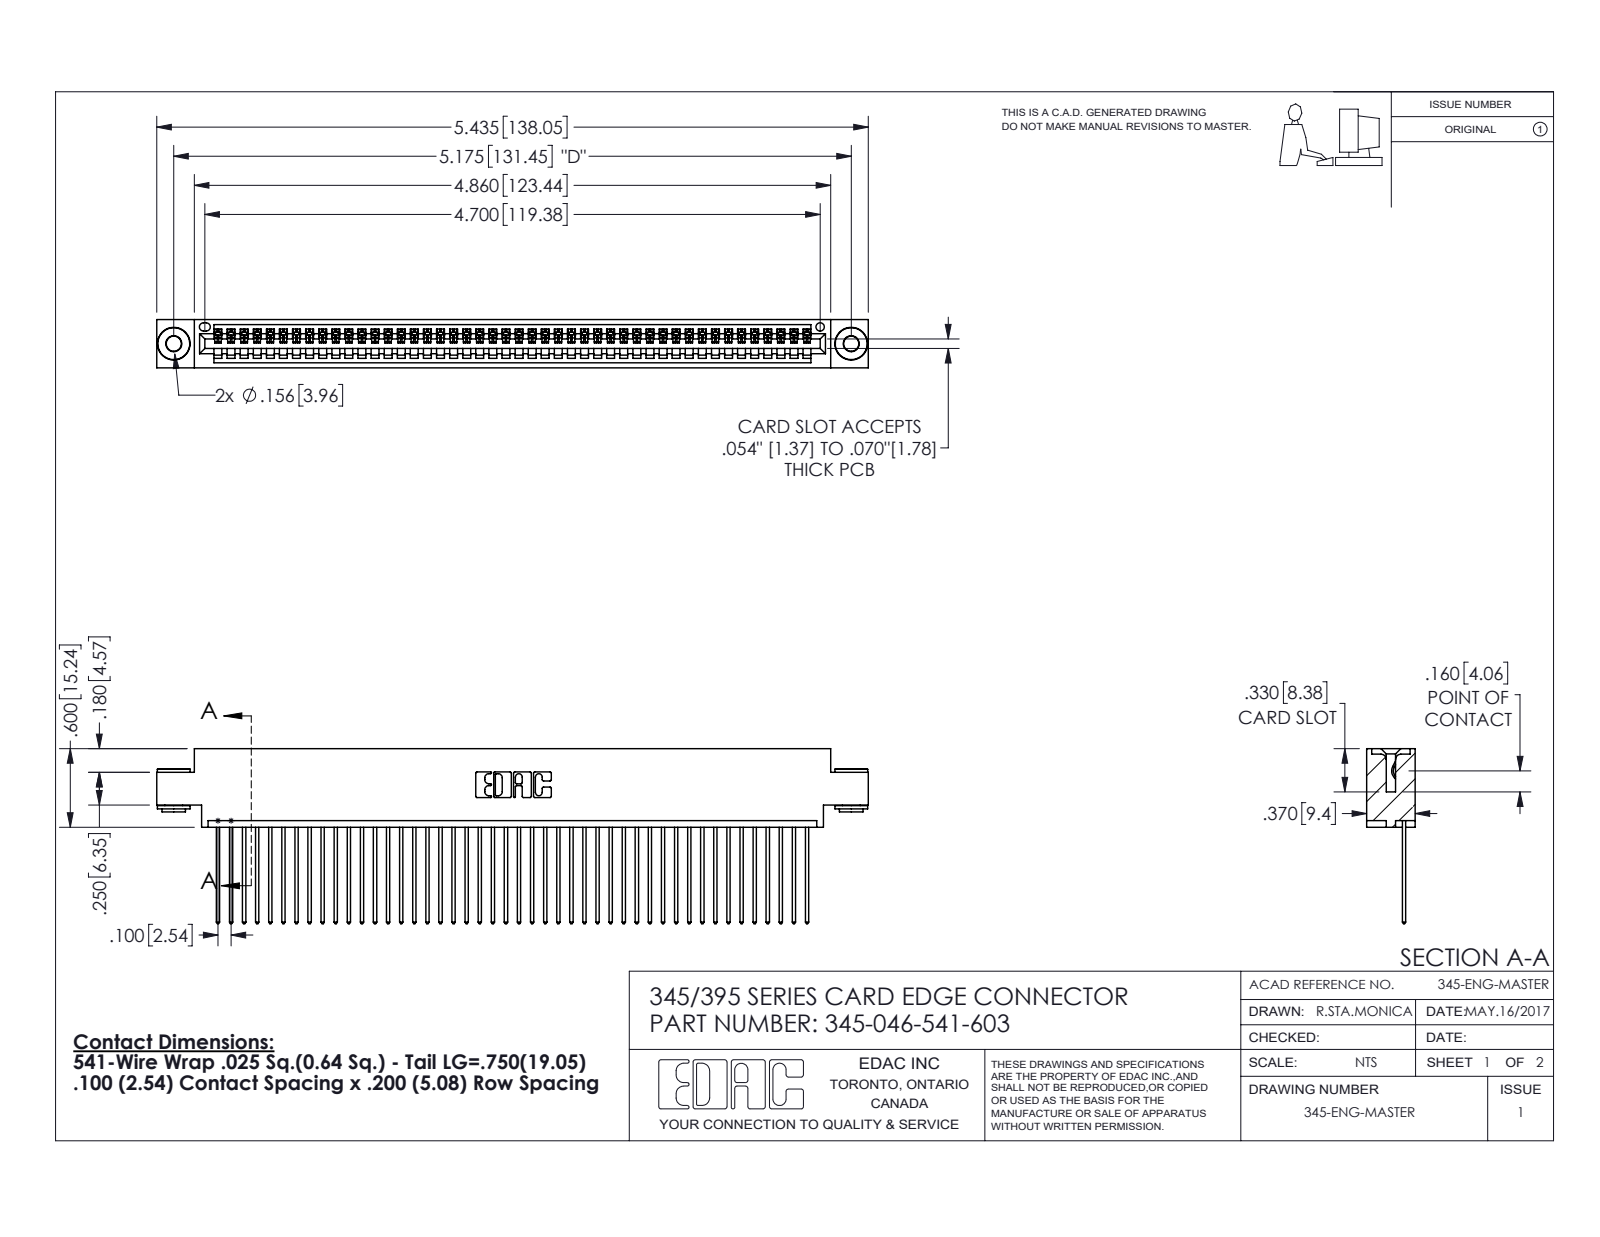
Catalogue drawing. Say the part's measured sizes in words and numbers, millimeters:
The part is named "345-292-001_345-293-141; 345-250-002_345-250-002-102; 345 Part_0.170 Offset - 0.156 Dia-TH; 345-046-541-603". Its 3-D file was written by "SolidWorks 2016 (CONFIG_CONTROL_DESIGN)". It is 49 solids with 2836 faces: 1934 planar, 894 cylindrical and 8 other. Overall it measures 138 by 34 by 9.4 millimeters. Its volume is 13 200 cubic millimeters and its surface area 18 830 square millimeters. Round holes: 2 of diameter 2.9, 2 of diameter 4, 1 of diameter 1.6. Round bosses or shafts: 2 of diameter 6.4, 2 of diameter 4.6, 2 of diameter 3.5. Partial cylindrical surfaces (rounded edges, fillets, slot ends): 92 of radius 0.2, 92 of radius 0.3, 22 of radius 0.3, 6 of radius 0.2, 6 of radius 0.8, 3 of radius 0.7, 2 of radius 0.8, 2 of radius 1. The main face-to-face distances are 1.8, 7.6, 9.4, 2.5, 6.9, 0.6, 5.1, 5.7, 4.4, 3.8. The hole center spacings are 6.9, 125.5, 131.4.
